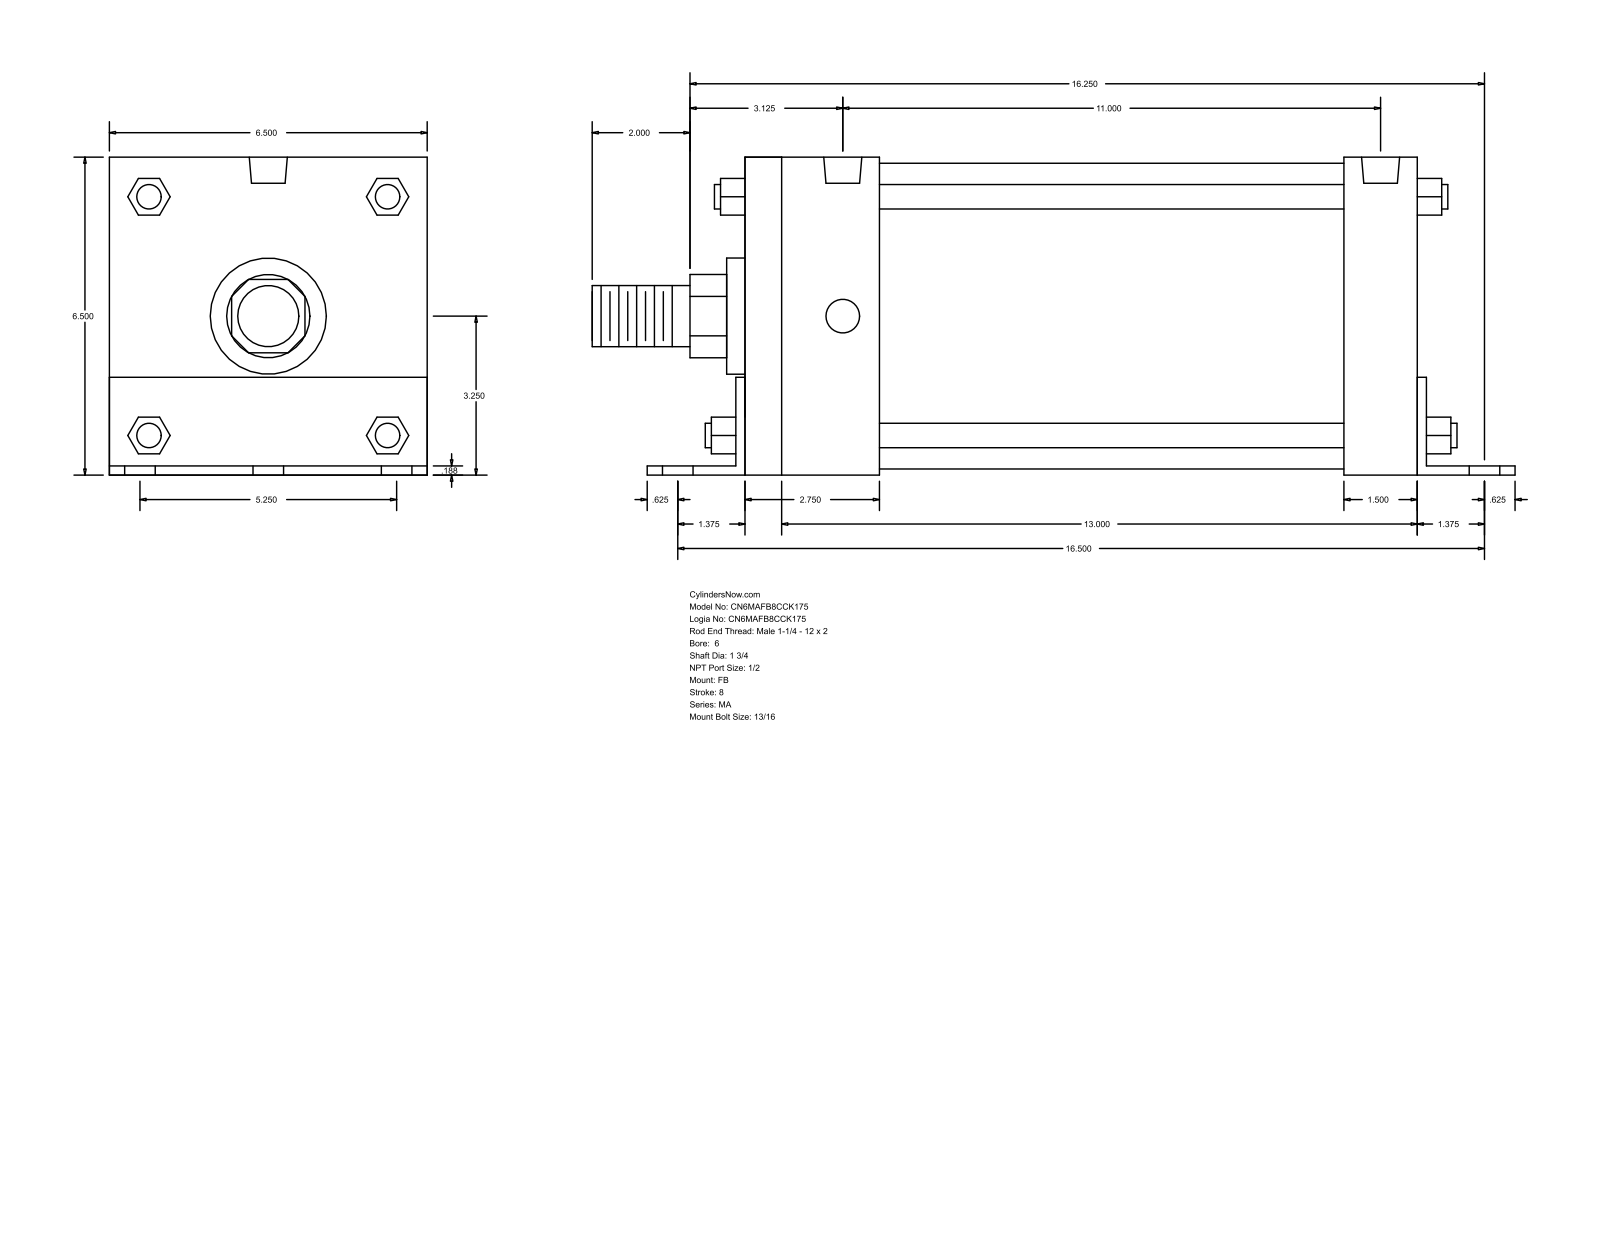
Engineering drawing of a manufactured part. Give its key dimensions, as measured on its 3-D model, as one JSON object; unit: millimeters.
{"part_name": "MA_FB__0600_1.75", "step_written_by": "GSSL Pune (CONFIG_CONTROL_DESIGN)", "units": "millimeters", "bodies": {"solids": 0, "faces": 140, "planar": 105, "cylindrical": 35, "other": 0}, "overall_size": [479.43, 165.15, 165.1], "round_holes": [[20.64, 6], [17.46, 4], [19.77, 2]], "round_bosses_or_shafts": [[12.7, 4], [158.75, 1], [60.33, 1], [44.45, 1], [31.75, 1]], "partial_cylinders_radius": [[21.63, 1], [32.05, 1]], "face_to_face_distances": [165.1, 4.76, 349.25, 165.15, 4.71, 160.39, 69.85, 74.61, 4.77, 354.02], "hole_center_spacings": [66.67, 424.37, 419.1, 85.78, 108.6, 133.34, 279.39, 339.97]}
